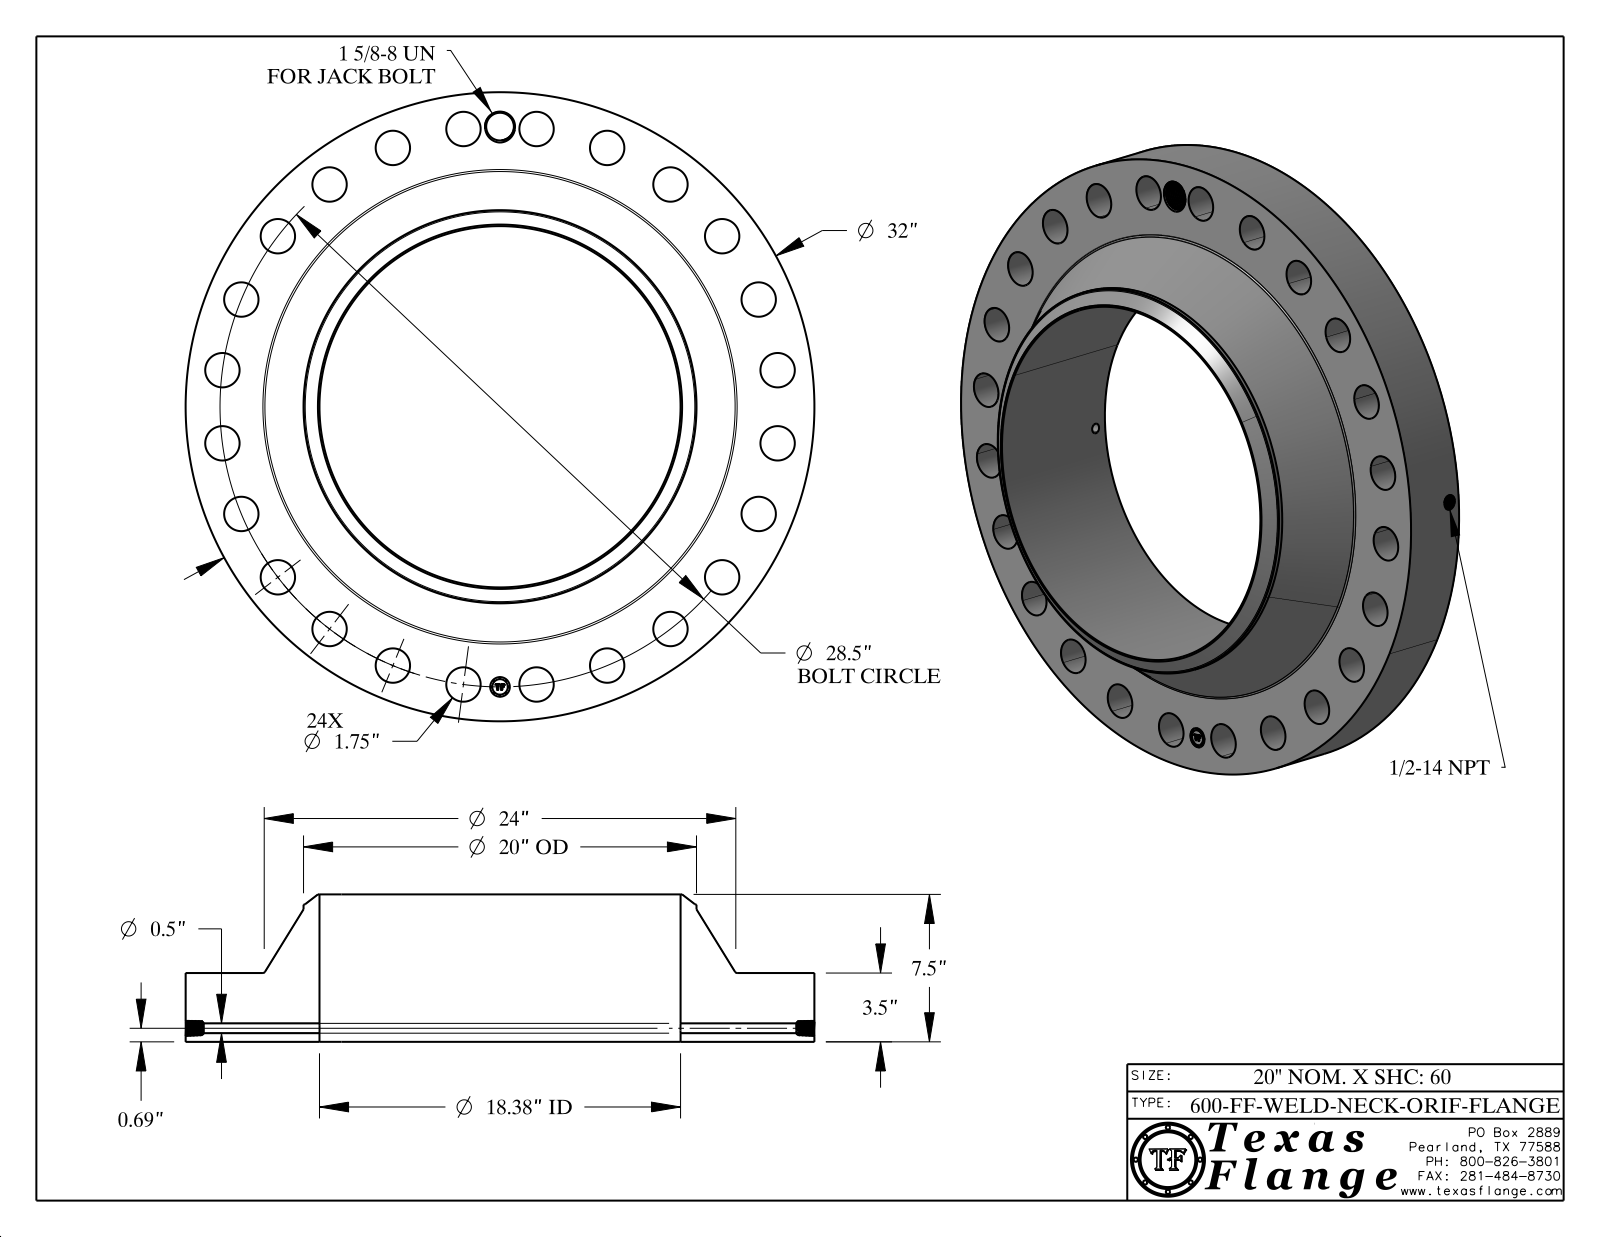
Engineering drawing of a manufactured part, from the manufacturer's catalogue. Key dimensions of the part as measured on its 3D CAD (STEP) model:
Part name (STEP PRODUCT): 600-FF-WELD-NECK
STEP written by: CATIA V5 STEP AP214 (AUTOMOTIVE_DESIGN)
Units: inches
Bodies: 1 solid, 880 faces (368 planar, 149 cylindrical, 363 other)
Overall size (bounding box): 32 × 32 × 7.5
Volume: 2 076 in³ · Surface area: 2 413 in²
Round holes (diameter × count): ⌀1.75 ×24, ⌀0.5 ×1, ⌀0.672 ×1, ⌀1 ×1, ⌀1.409 ×1, ⌀18.376 ×1
Round bosses / shafts (diameter × count): ⌀0.061 ×8, ⌀32 ×1, ⌀20 ×1, ⌀0.788 ×1
Main face-to-face distances: 3.5, 7.5, 4, 3.485, 0.015, 4.015, 0.298, 0.293, 0.054, 0.248
Hole centre spacings: 14.25, 17.35, 24.681, 28.256, 10.906, 3.72, 7.376, 20.152
